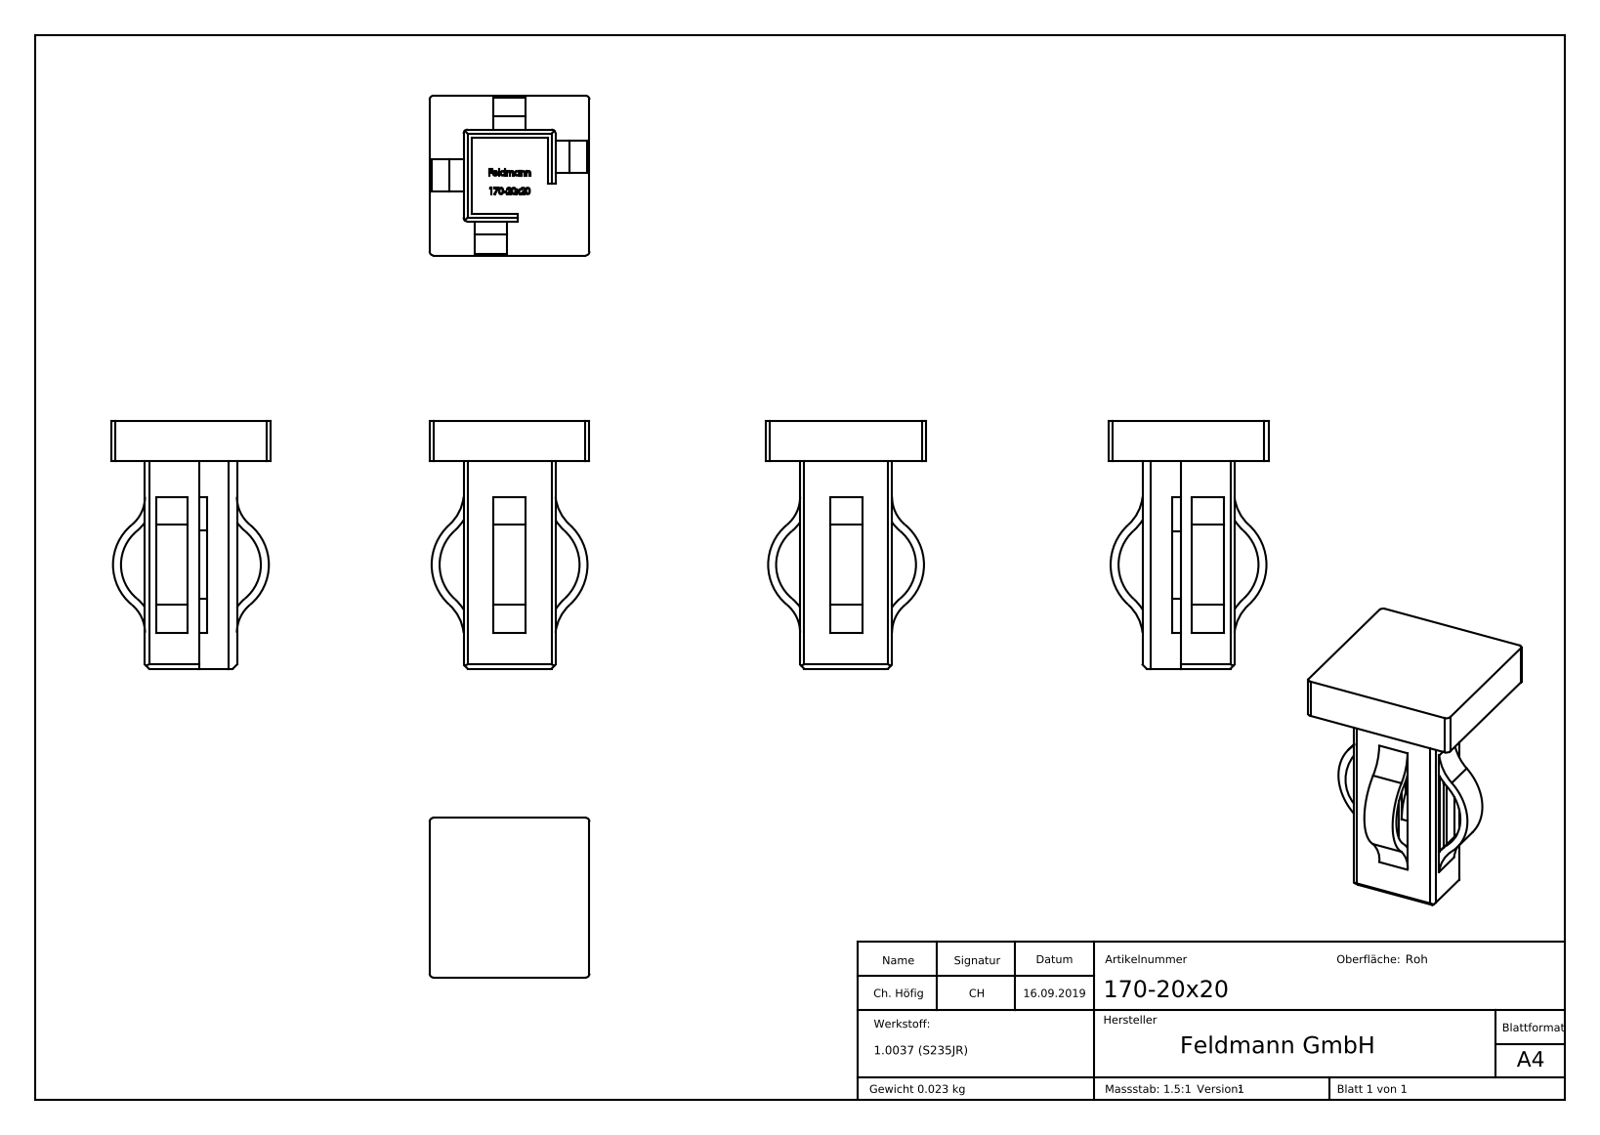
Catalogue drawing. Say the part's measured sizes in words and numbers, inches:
The part is named "170-20x20". Its 3-D file was written by "SolidWorks 2015 (CONFIG_CONTROL_DESIGN)". It is 1 solid with 276 faces: 154 planar, 35 cylindrical and 87 other. Overall it measures 1.22 by 0.787 by 0.787 inches. Its volume is 0.177 cubic inches and its surface area 5.067 square inches. Partial cylindrical surfaces (rounded edges, fillets, slot ends): 7 of radius 0.02, 4 of radius 0.179, 4 of radius 0.218, 4 of radius 0.22, 4 of radius 0.259, 2 of radius 0.216, 2 of radius 0.227, 2 of radius 0.256. The main face-to-face distances are 0.039, 0.167, 0.62, 0.197, 0.207, 0.581, 0.413, 0.787, 0.453, 0.148.
